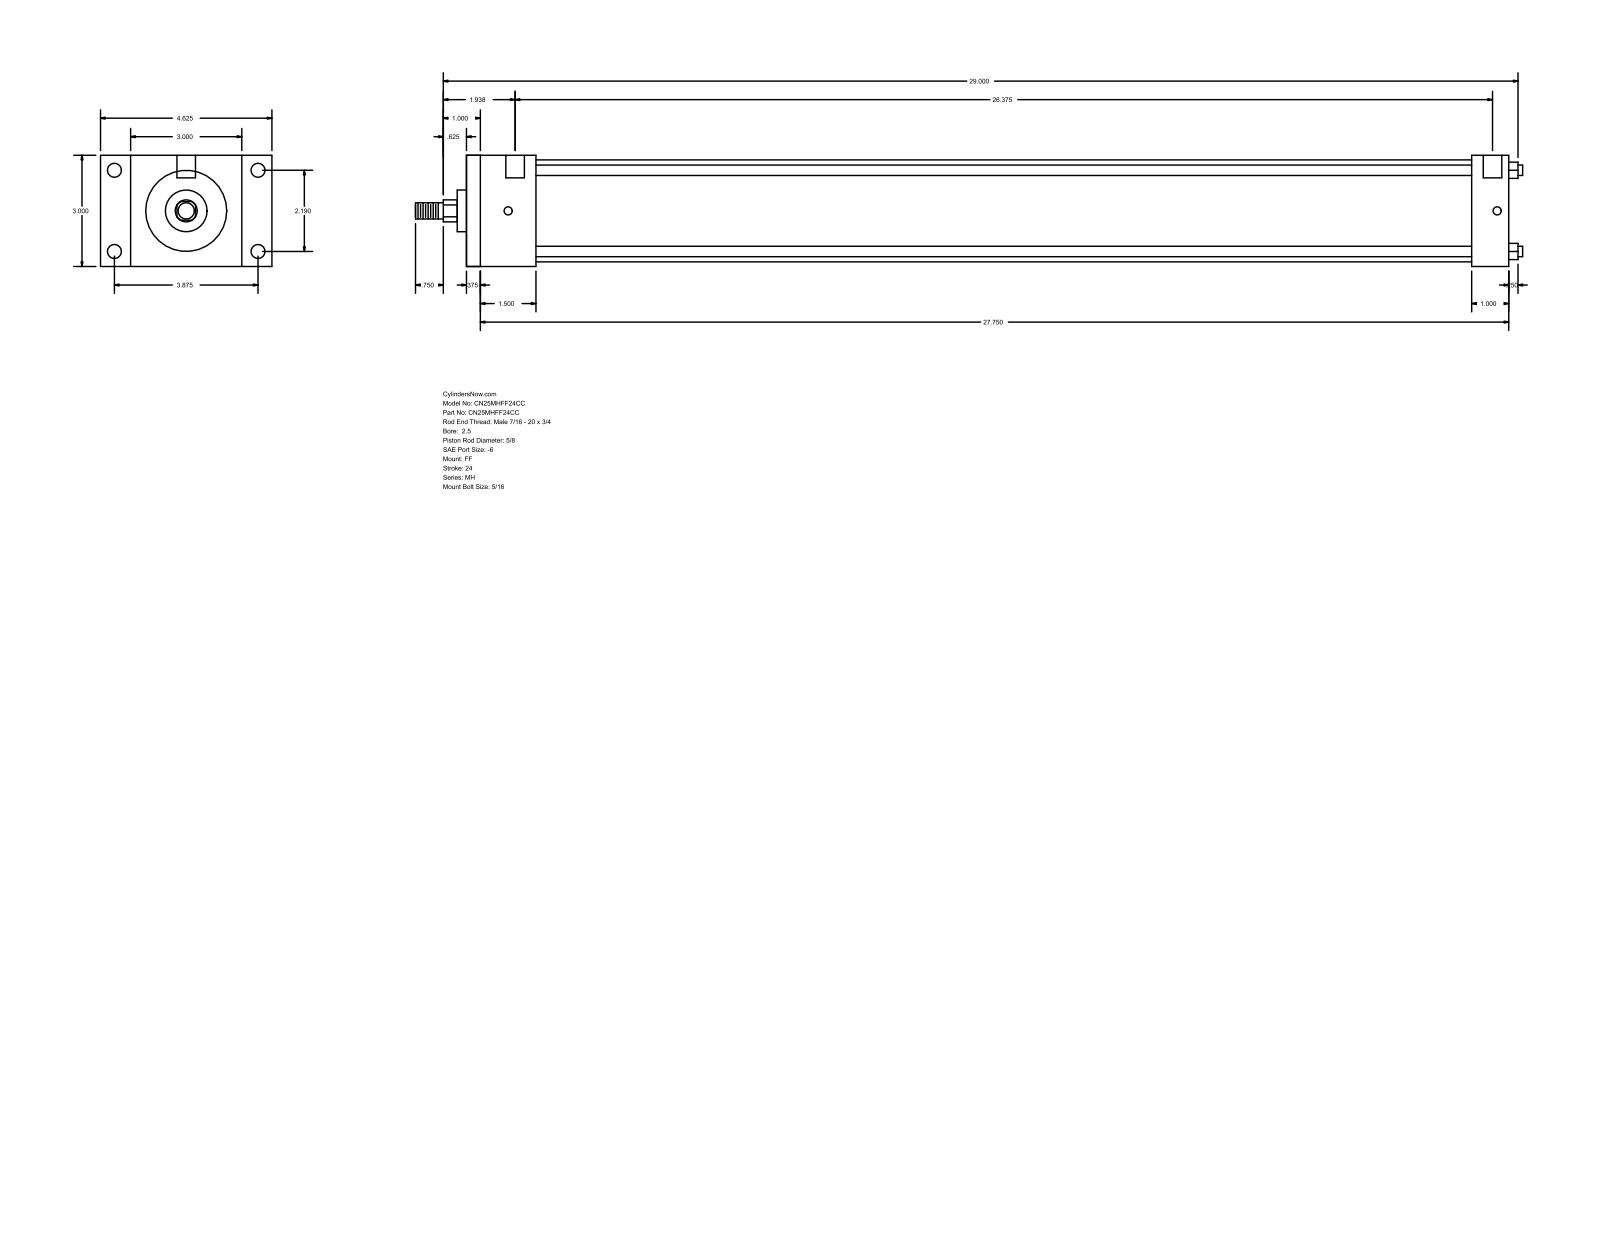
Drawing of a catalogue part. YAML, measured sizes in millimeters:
part_name: "MH_FF__0250_0.625"
step_written_by: "GSSL Pune (CONFIG_CONTROL_DESIGN)"
units: millimeters
bodies: {solids: 0, faces: 92, planar: 64, cylindrical: 28, other: 0}
overall_size: [758.83, 117.47, 76.2]
round_holes:
  - {diameter: 5.56, count: 4}
  - {diameter: 9.53, count: 4}
  - {diameter: 12.7, count: 2}
round_bosses_or_shafts:
  - {diameter: 7.14, count: 4}
  - {diameter: 69.85, count: 1}
  - {diameter: 28.57, count: 1}
  - {diameter: 15.88, count: 1}
  - {diameter: 11.11, count: 1}
partial_cylinders:
  - {radius: 7.54, count: 1}
face_to_face_distances: [76.2, 714.37, 9.52, 704.85, 25.4, 47.62, 688.97, 38.1, 679.45, 641.35]
hole_center_spacings: [55.62, 98.42, 113.05, 677.86, 3.17, 4.76, 669.93, 673.1]
